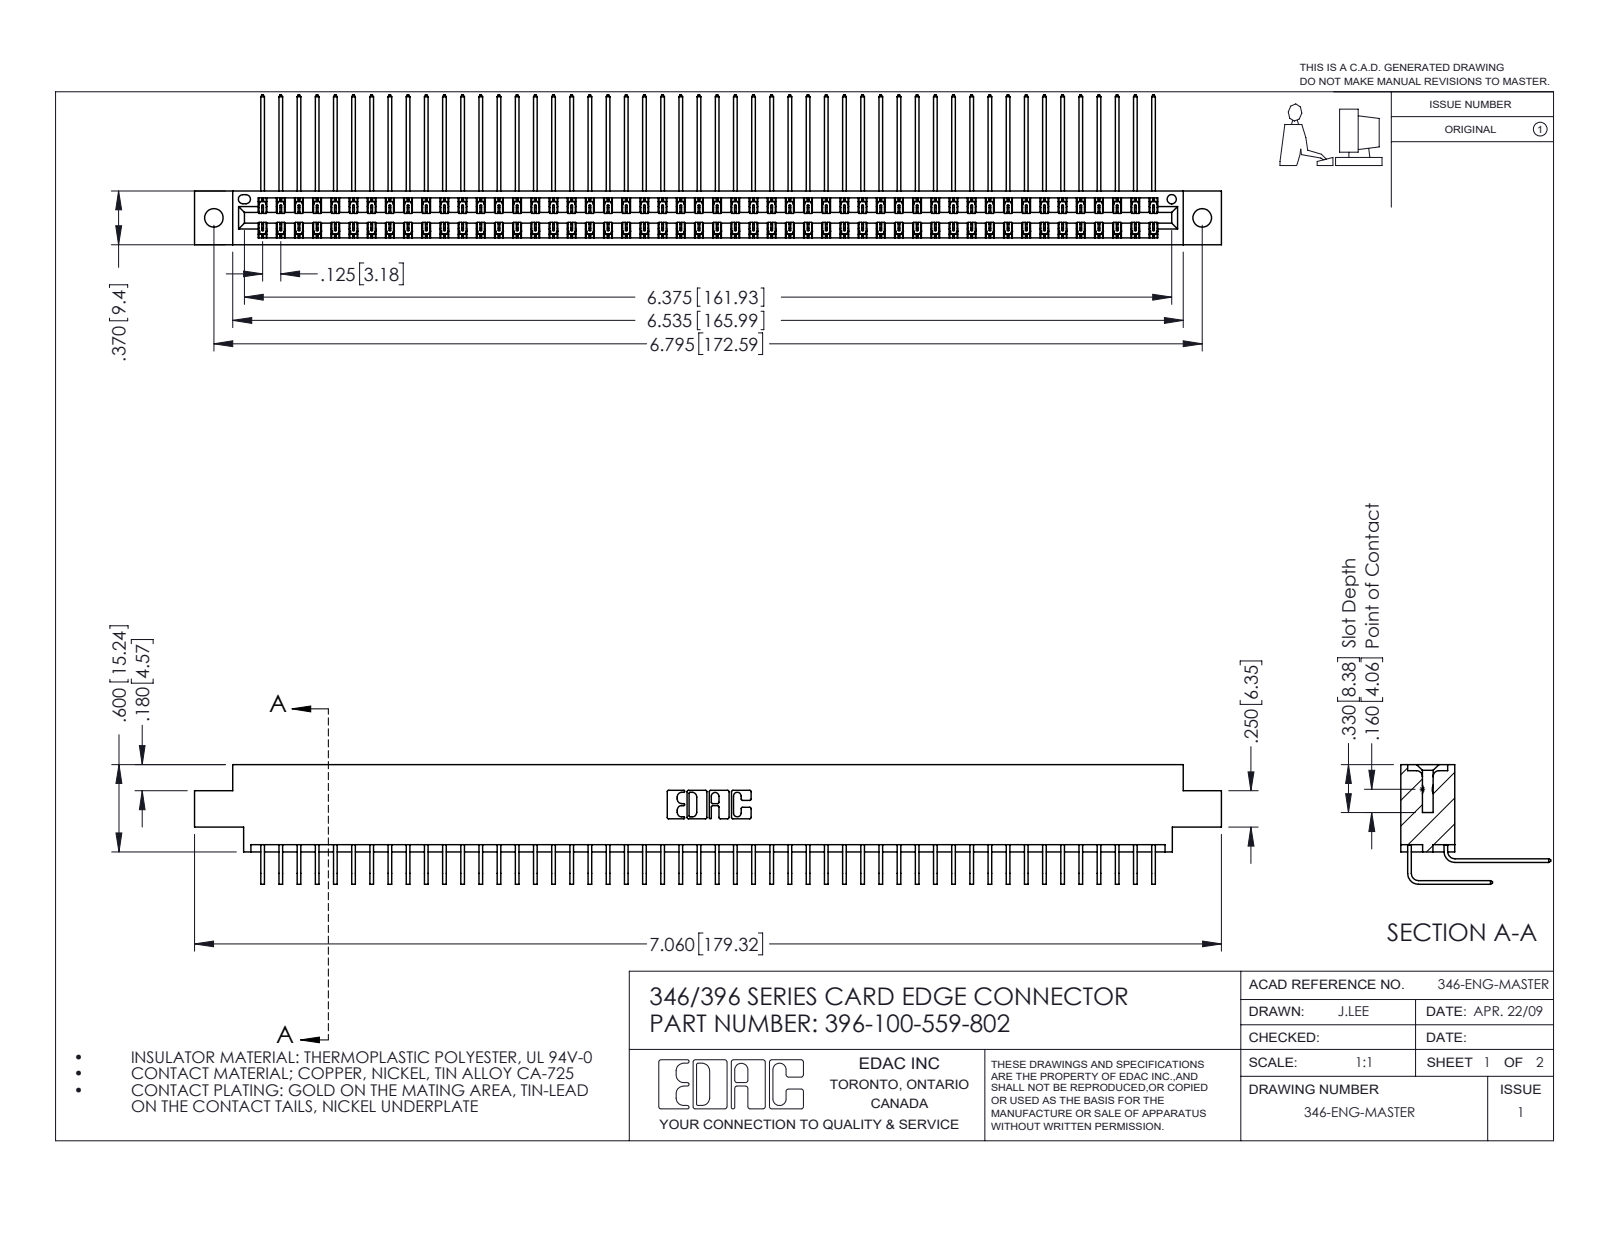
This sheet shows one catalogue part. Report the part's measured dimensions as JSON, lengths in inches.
{"part_name": "346 Part_0.170 Offset - 0.128 Dia; 396-100-559-802; 345-292-001_558 559 Tail - 1; 345-292-001_559 Tail - 2", "step_written_by": "SolidWorks 2016 (CONFIG_CONTROL_DESIGN)", "units": "inches", "bodies": {"solids": 101, "faces": 5526, "planar": 3780, "cylindrical": 1746, "other": 0}, "overall_size": [7.06, 1.03, 0.823], "volume_in3": 1.094, "surface_area_in2": 42.56, "round_holes": [[0.128, 2], [0.064, 1]], "partial_cylinders_radius": [[0.006, 150], [0.01, 22], [0.007, 6], [0.031, 6], [0.026, 3], [0.014, 2], [0.022, 2], [0.024, 2]], "face_to_face_distances": [0.048, 0.322, 0.025, 0.37, 0.25, 0.072, 0.298, 0.275, 0.148, 0.222], "hole_center_spacings": [0.246, 6.586, 6.795]}
